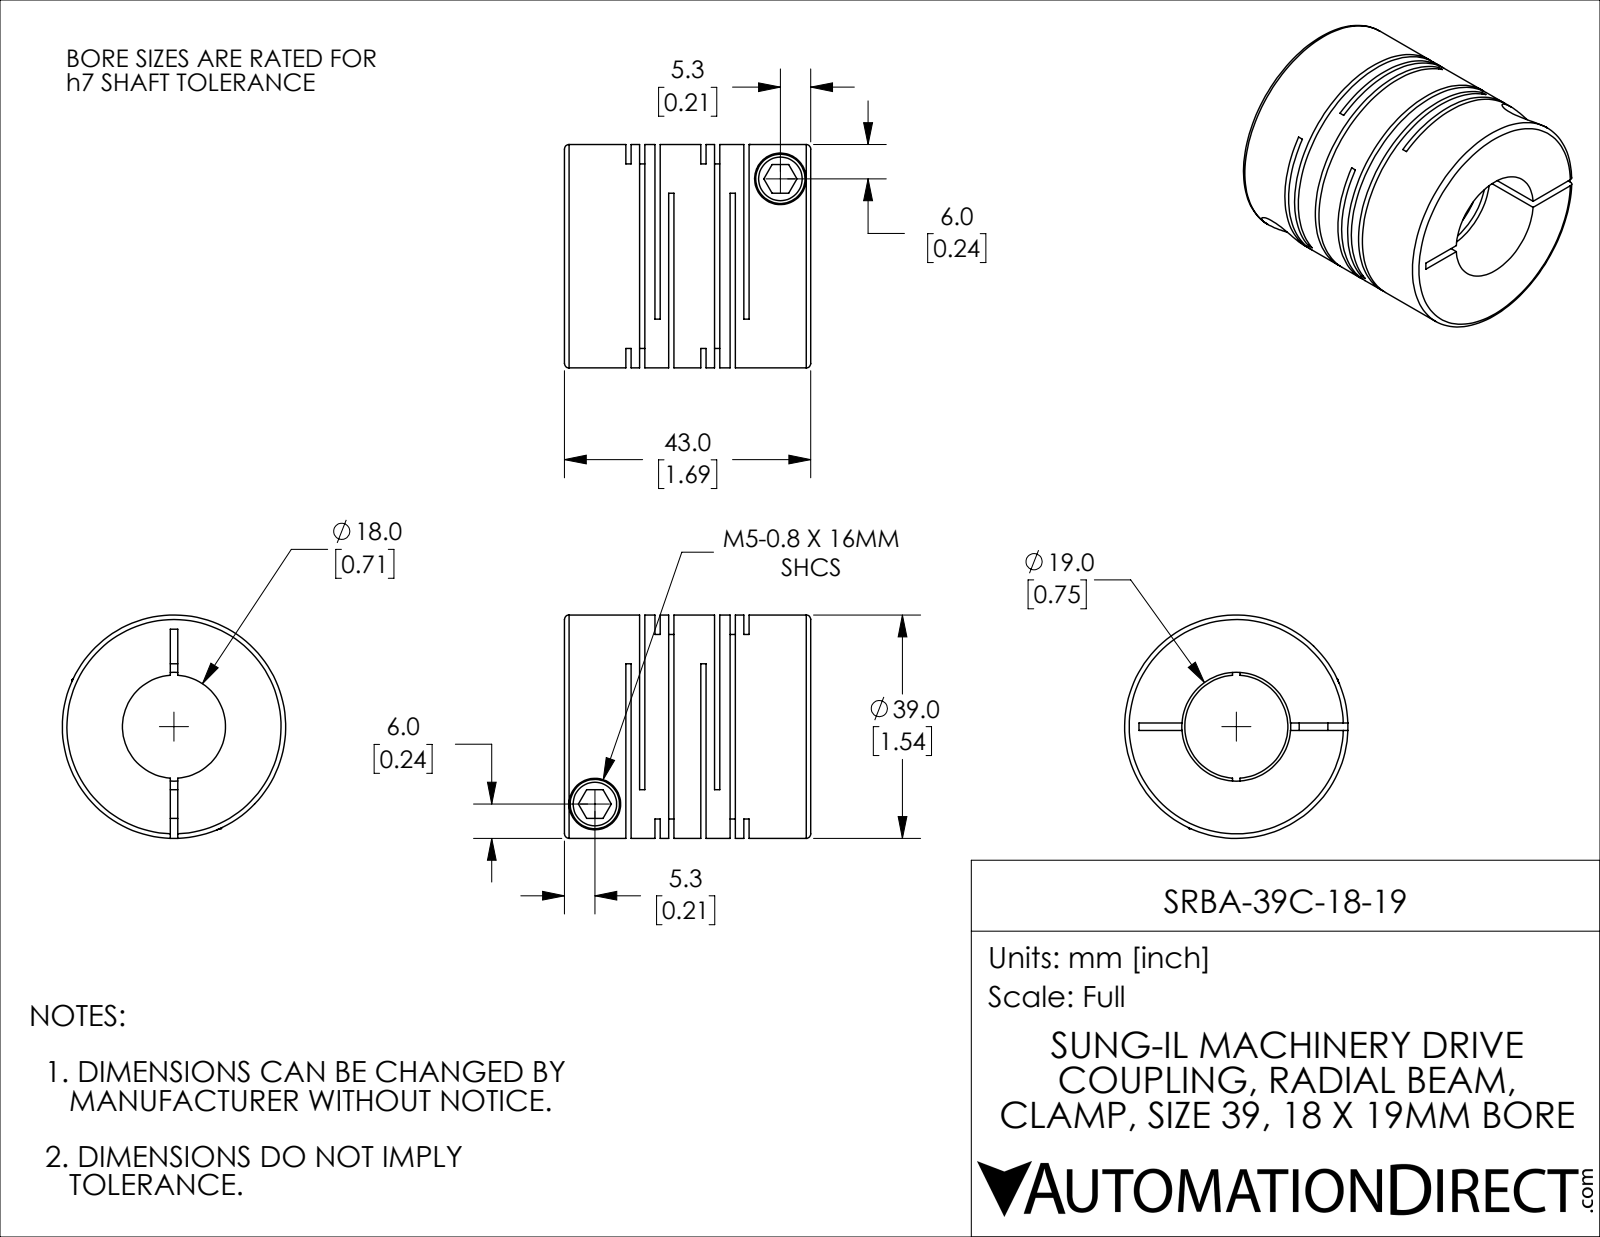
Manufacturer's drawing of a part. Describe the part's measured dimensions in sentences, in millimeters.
The part is named "SRBA-39C-18-19". Its 3-D file was written by "SolidWorks 2021 (CONFIG_CONTROL_DESIGN)". It is 1 solid with 114 faces: 60 planar, 42 cylindrical and 12 other. Overall it measures 43 by 39 by 39 millimeters. Its volume is 32 785 cubic millimeters and its surface area 21 718 square millimeters. Round holes: 2 of diameter 5, 2 of diameter 9, 1 of diameter 18, 1 of diameter 19. Round bosses or shafts: 2 of diameter 8.6, 1 of diameter 39. The main face-to-face distances are 13.1, 0.92, 2.4, 5.1, 10.7, 14.02, 18.2, 3.32, 15.5, 1.48.
